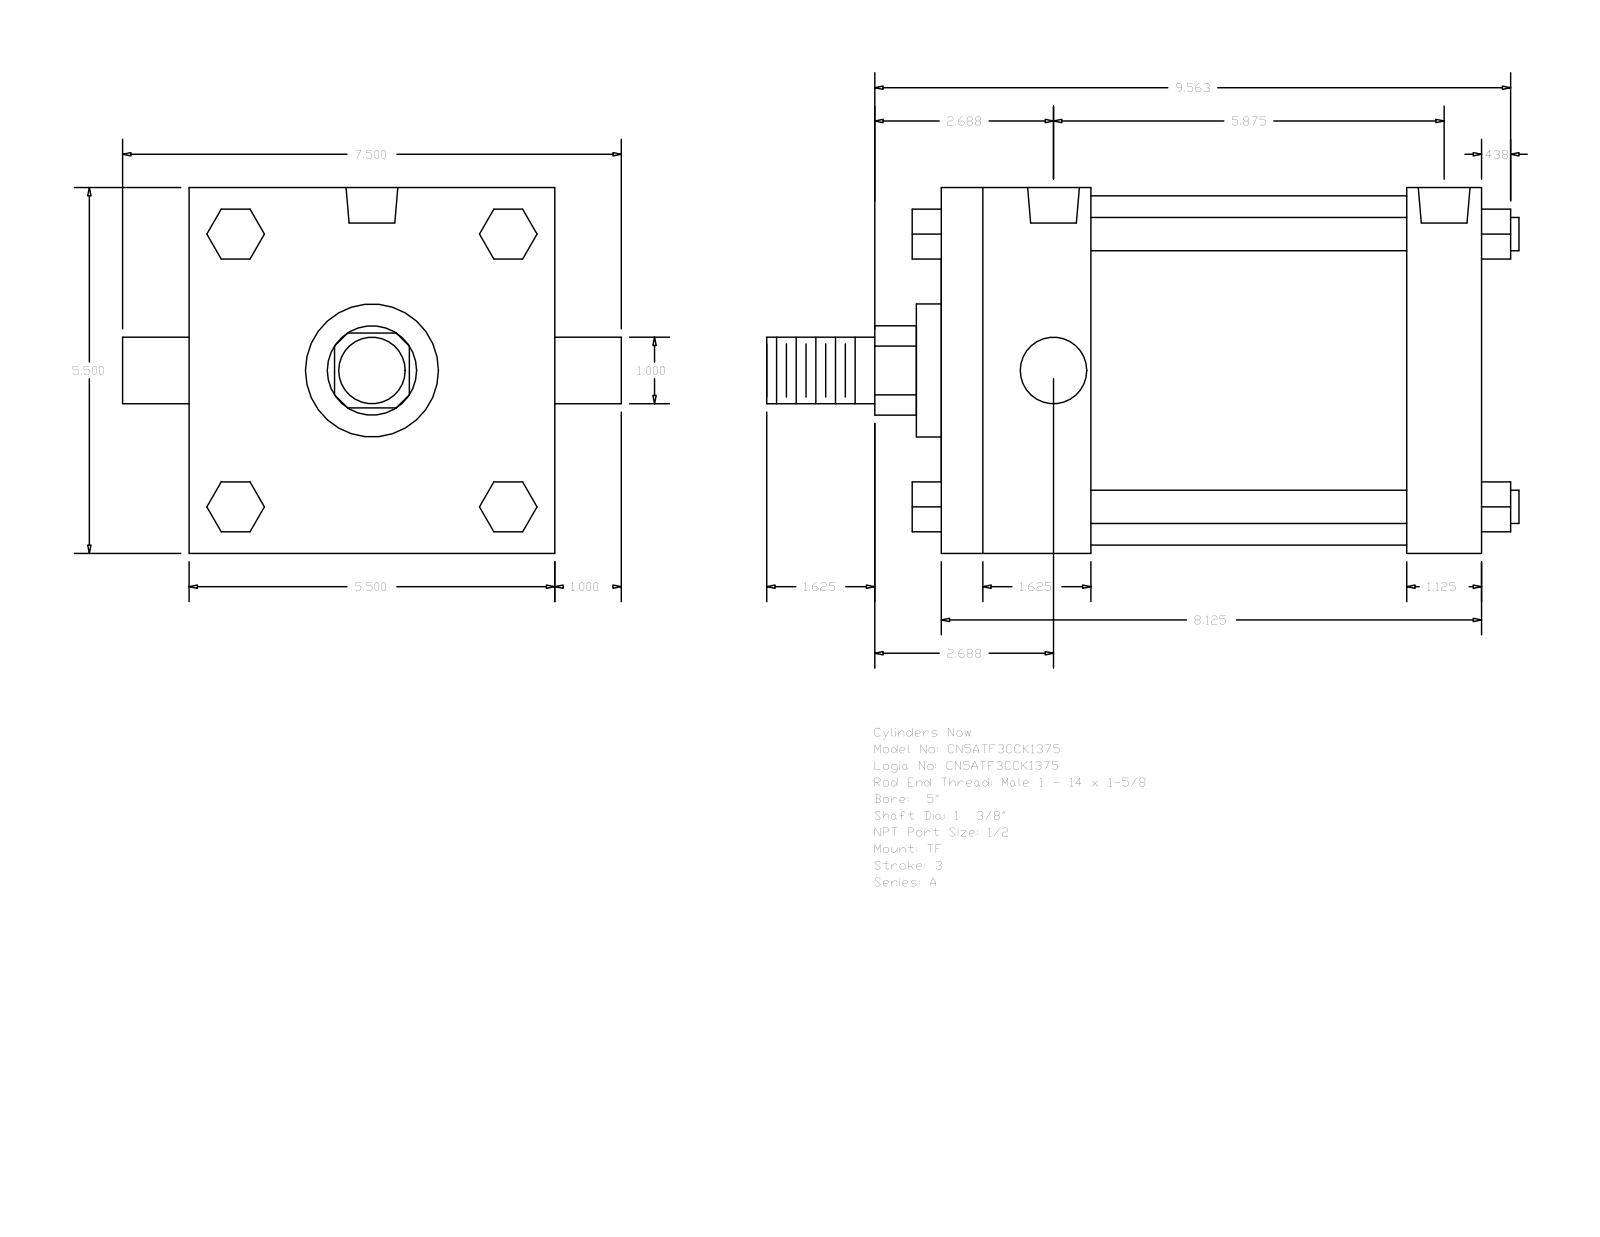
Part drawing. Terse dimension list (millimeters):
name: A_TF__0500_1.375
written by: GSSL Pune (CONFIG_CONTROL_DESIGN)
unit: mm
bodies: 0 solids, 120 faces (92 planar, 28 cylindrical, 0 other)
size: 287.34 × 190.5 × 139.7
holes: 3× ⌀8.73, 2× ⌀19.77
bosses: 4× ⌀12.7, 2× ⌀25.4, 1× ⌀133.35, 1× ⌀50.8, 1× ⌀34.92
rounds: 1× R17.06
face distances: 139.7, 206.38, 57.15, 28.58, 177.8, 120.65, 149.23, 19.05, 52.07, 90.18
hole spacings: 2.39, 146.84, 144.45, 149.23
